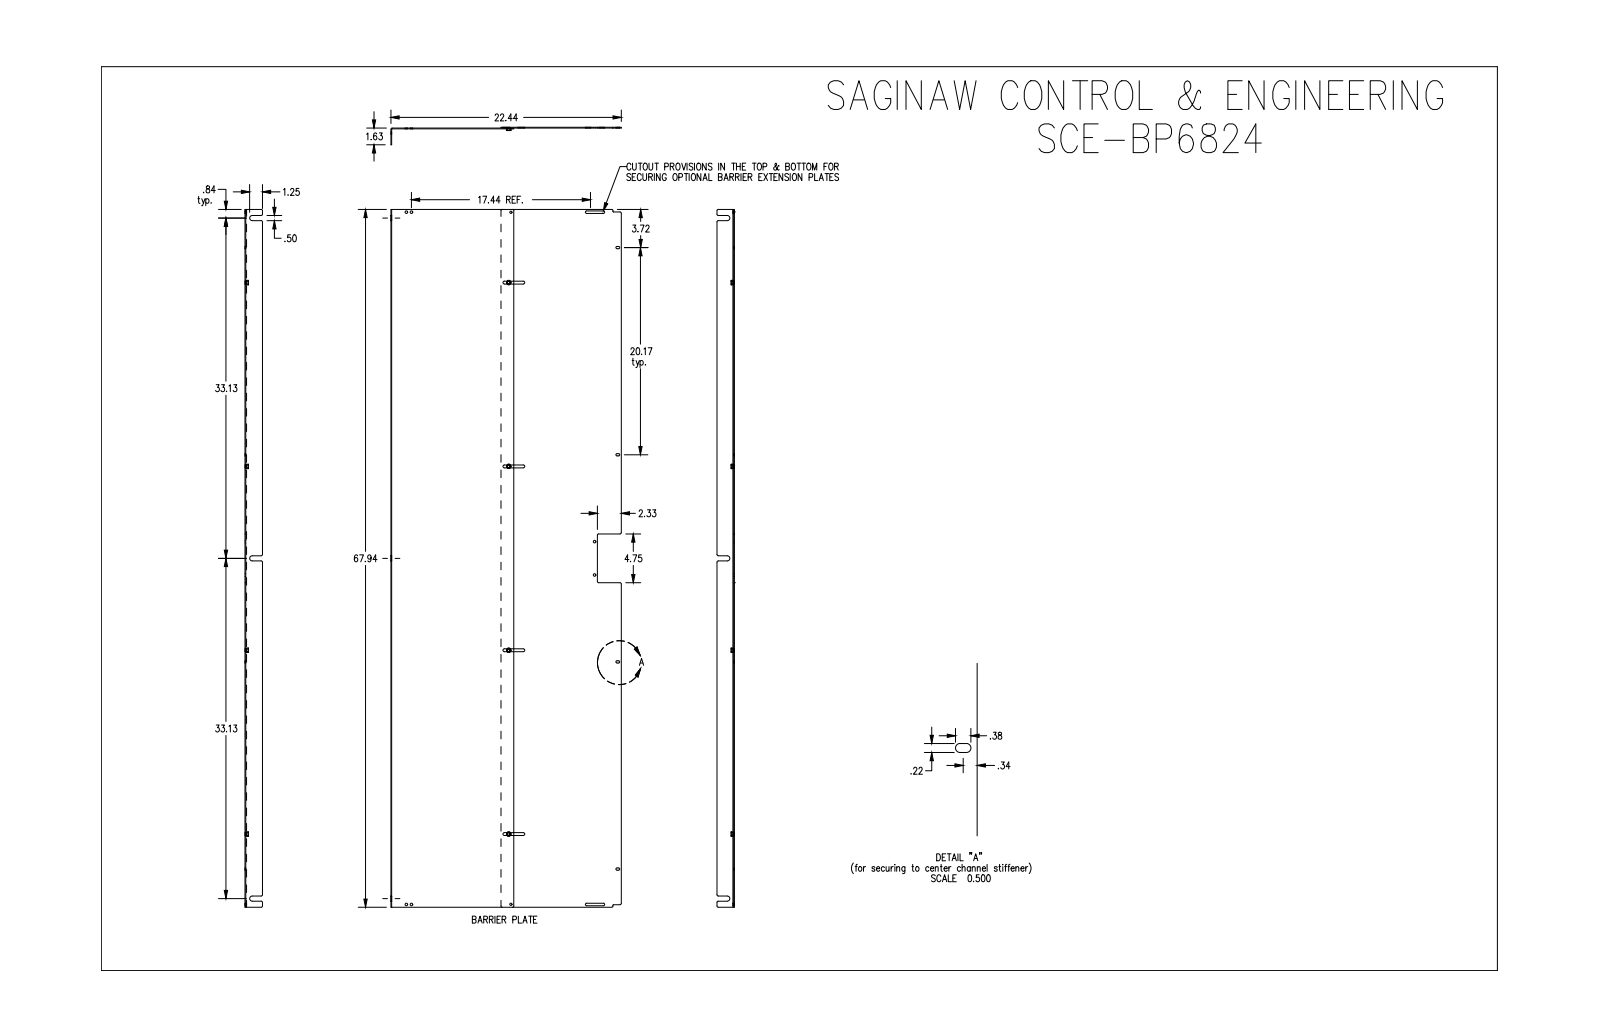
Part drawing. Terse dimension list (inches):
name: SCE-BP6824
written by: SolidWorks 2019 (CONFIG_CONTROL_DESIGN)
unit: in
bodies: 6 solids, 146 faces (63 planar, 71 cylindrical, 12 other)
size: 67.937 × 22.44 × 1.7
volume: 127.2 in³; area: 3 420 in²
holes: 10× ⌀0.25, 4× ⌀0.344, 2× ⌀0.218
bosses: 4× ⌀0.44, 4× ⌀0.343
rounds: 24× R0.125, 8× R0.109, 8× R0.141, 3× R0.25, 2× R0.062, 1× R0.042, 1× R0.117
face distances: 0.075, 0.15, 10.72, 10.645, 11.97, 11.895, 1.25, 1.7, 1.625, 1.55
hole spacings: 0.5, 6.847, 9.689, 10.189, 11.121, 11.691, 12.099, 13.485
